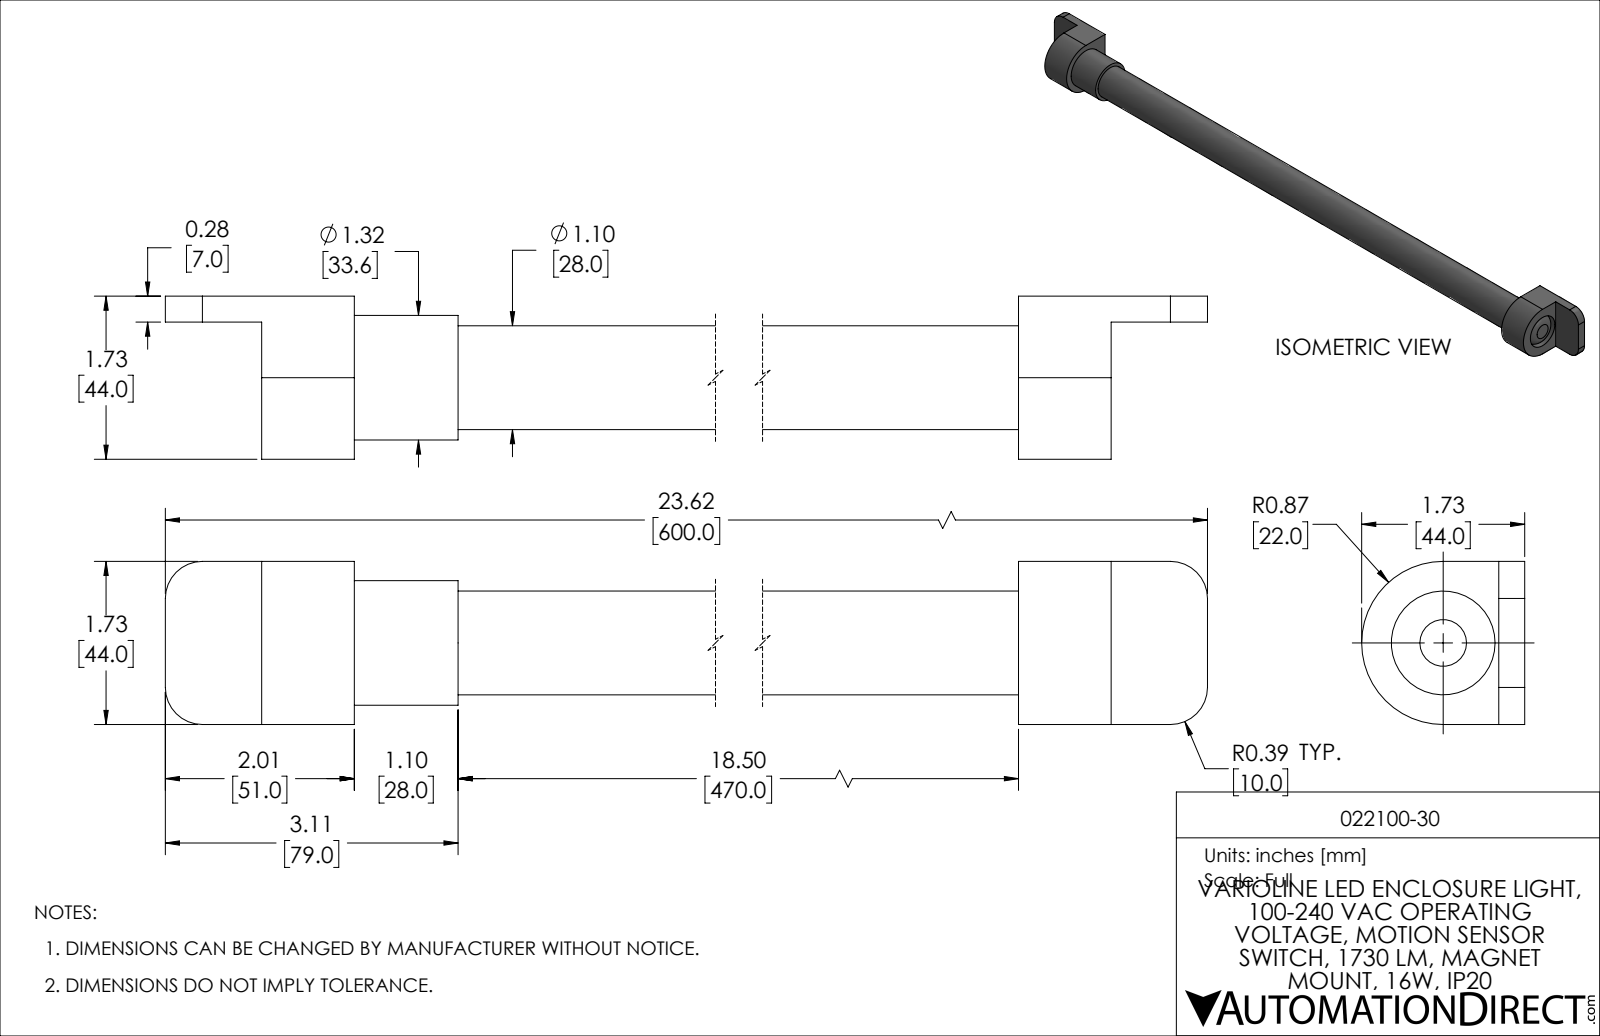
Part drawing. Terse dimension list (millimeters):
name: PRODUCT_NAME_1
written by: ACIS (AUTOMOTIVE_DESIGN_CC2)
unit: mm
bodies: 1 solid, 35 faces (17 planar, 14 cylindrical, 4 other)
size: 600 × 44 × 44
volume: 414 083 mm³; area: 64 923 mm²
holes: 1× ⌀28
bosses: 1× ⌀33.6
rounds: 4× R10, 1× R22
face distances: 7, 25, 523, 44, 548, 498, 26, 51, 549, 574
